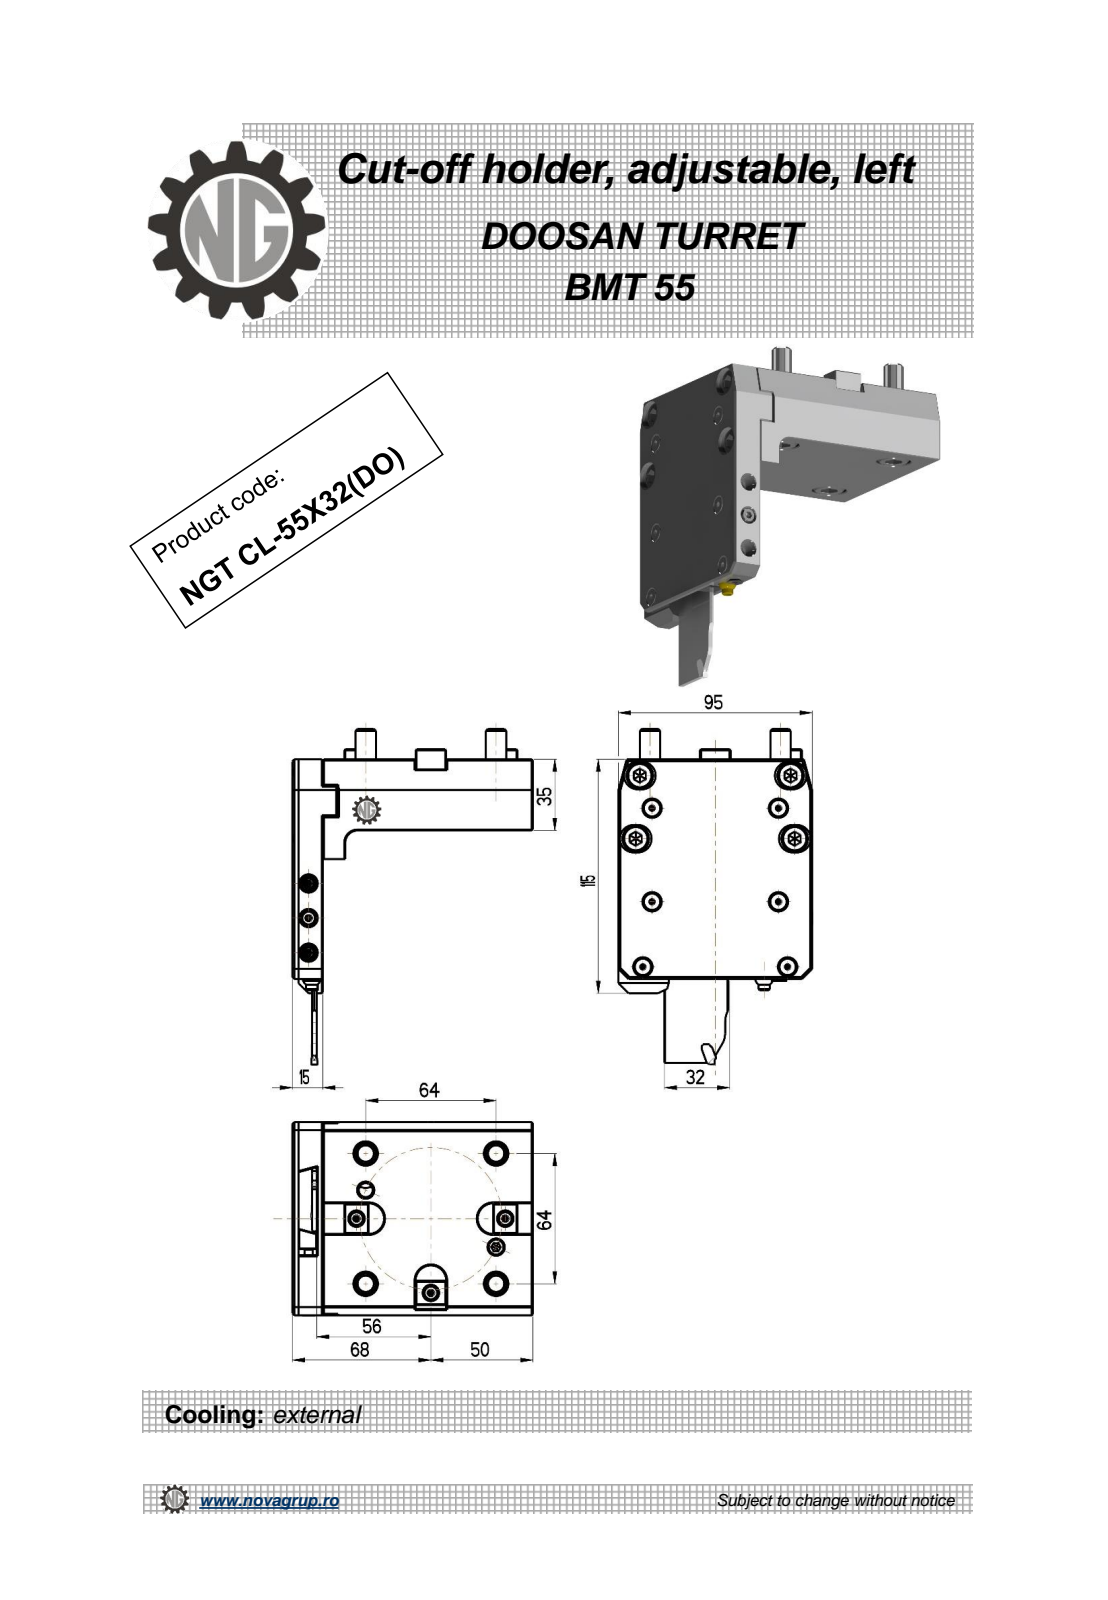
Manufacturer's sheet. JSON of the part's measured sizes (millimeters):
{"part_name": "NGT_CL_55_32_DO", "step_written_by": "PRO/ENGINEER BY PARAMETRIC TECHNOLOGY CORPORATION, 2010280 (CONFIG_CONTROL_DESIGN)", "units": "millimeters", "bodies": {"solids": 1, "faces": 440, "planar": 284, "cylindrical": 89, "other": 67}, "overall_size": [130, 118, 95.13], "volume_mm3": 458562, "surface_area_mm2": 76196, "round_holes": [[6.8, 3], [3.5, 1]], "round_bosses_or_shafts": [[13, 4], [10, 4], [4, 3], [8, 1], [5.5, 1]], "partial_cylinders_radius": [[0.26, 24], [6.75, 8], [0.14, 6], [0.16, 6], [0.41, 6], [7.5, 3], [6, 1], [60, 1]], "face_to_face_distances": [12, 3, 35, 15, 9, 95, 103, 115, 106, 118], "hole_center_spacings": [46.33, 78]}
